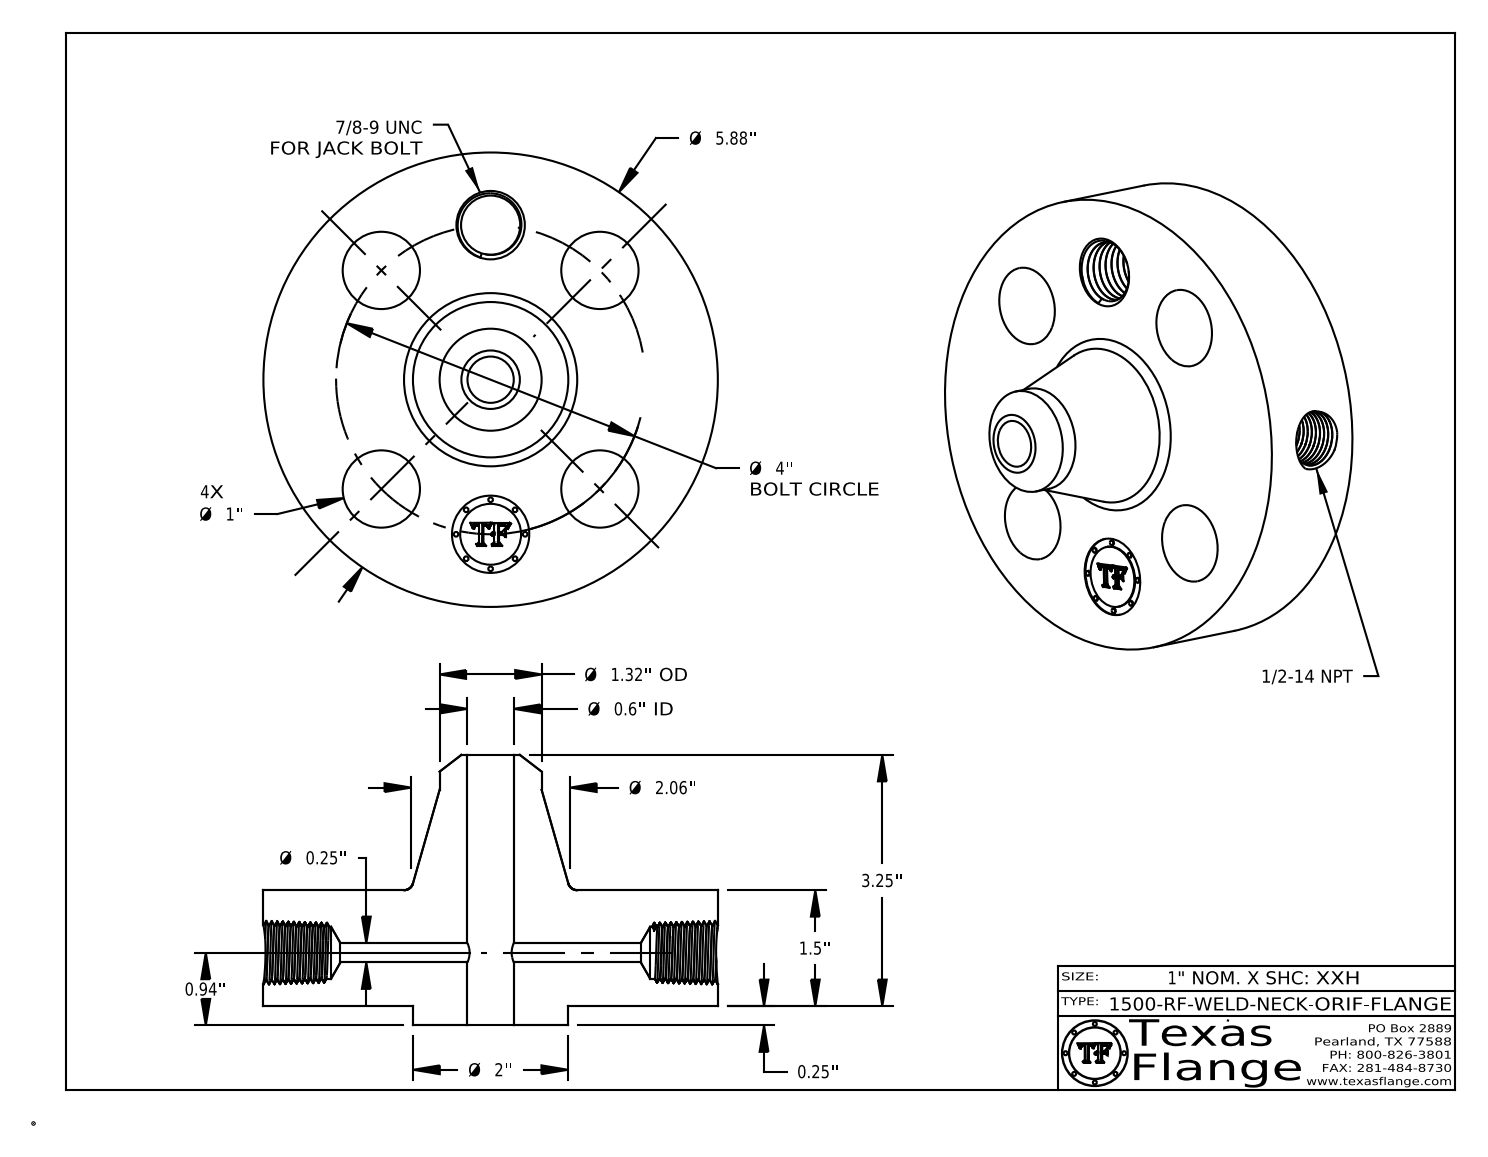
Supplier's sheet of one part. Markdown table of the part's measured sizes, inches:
| quantity | value |
| --- | --- |
| part name | 1500-RF-WELD-NECK |
| STEP written by | CATIA V5 STEP AP214 (AUTOMOTIVE_DESIGN) |
| units | inches |
| bodies | 1 solid, 749 faces (369 planar, 82 cylindrical, 298 other) |
| overall size | 5.88 × 5.88 × 3.5 |
| volume | 37.56 in³ |
| surface area | 122.3 in² |
| round holes (diameter × count) | 1 × 5, 0.25 × 1, 0.599 × 1, 0.672 × 1, 0.766 × 1 |
| round bosses / shafts (diameter × count) | 0.061 × 8, 5.88 × 1, 2 × 1, 1.32 × 1, 0.788 × 1 |
| main face-to-face distances | 1.5, 1.75, 0.25, 1.735, 1.485, 0.015, 3.5, 3.25, 1.765, 0.298 |
| hole center spacings | 2, 1.531, 2.828, 3.695, 4 |
